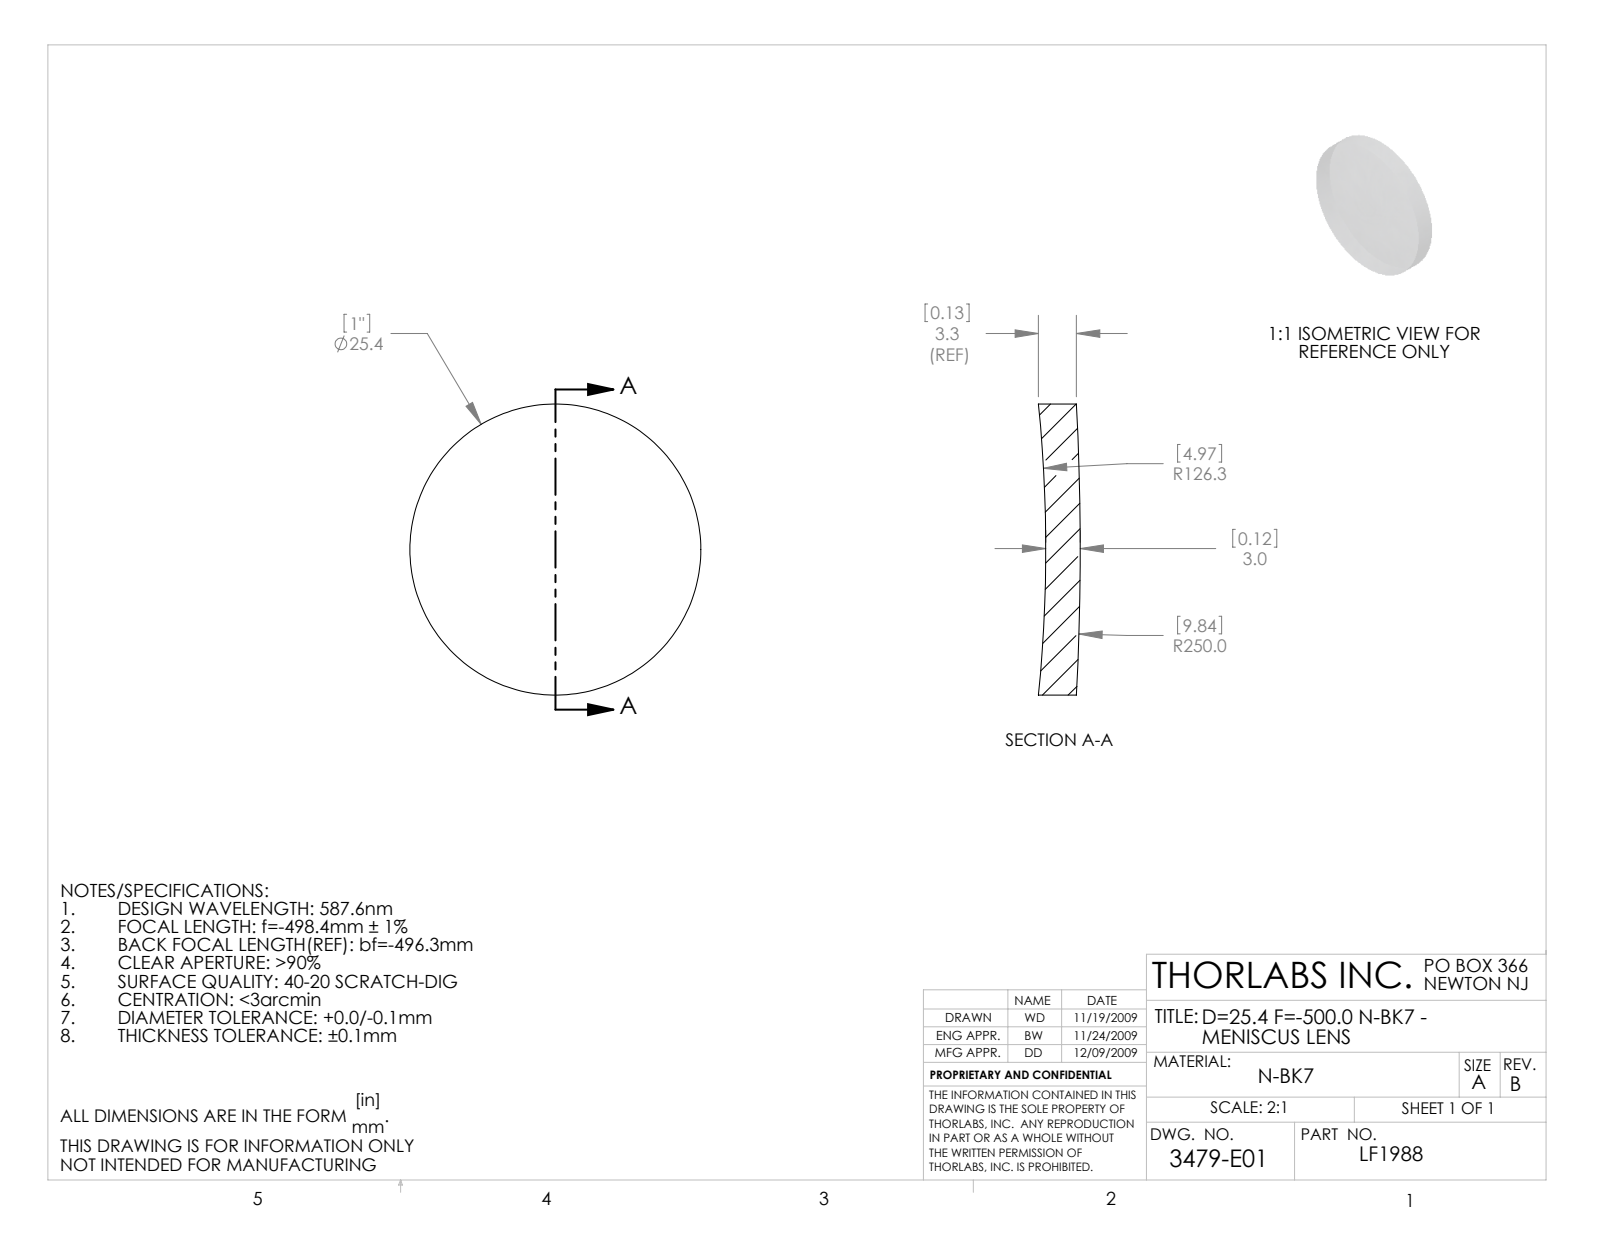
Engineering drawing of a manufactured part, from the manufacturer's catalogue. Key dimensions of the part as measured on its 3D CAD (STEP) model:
Part name (STEP PRODUCT): 3479-E0W
STEP written by: SolidWorks 2009 (AUTOMOTIVE_DESIGN)
Units: millimetres
Bodies: 1 solid, 6 faces (0 planar, 2 cylindrical, 4 other)
Overall size (bounding box): 25.4 × 25.4 × 3.64
Volume: 1 600 mm³ · Surface area: 1 280 mm²
Round bosses / shafts (diameter × count): ⌀25.4 ×1
